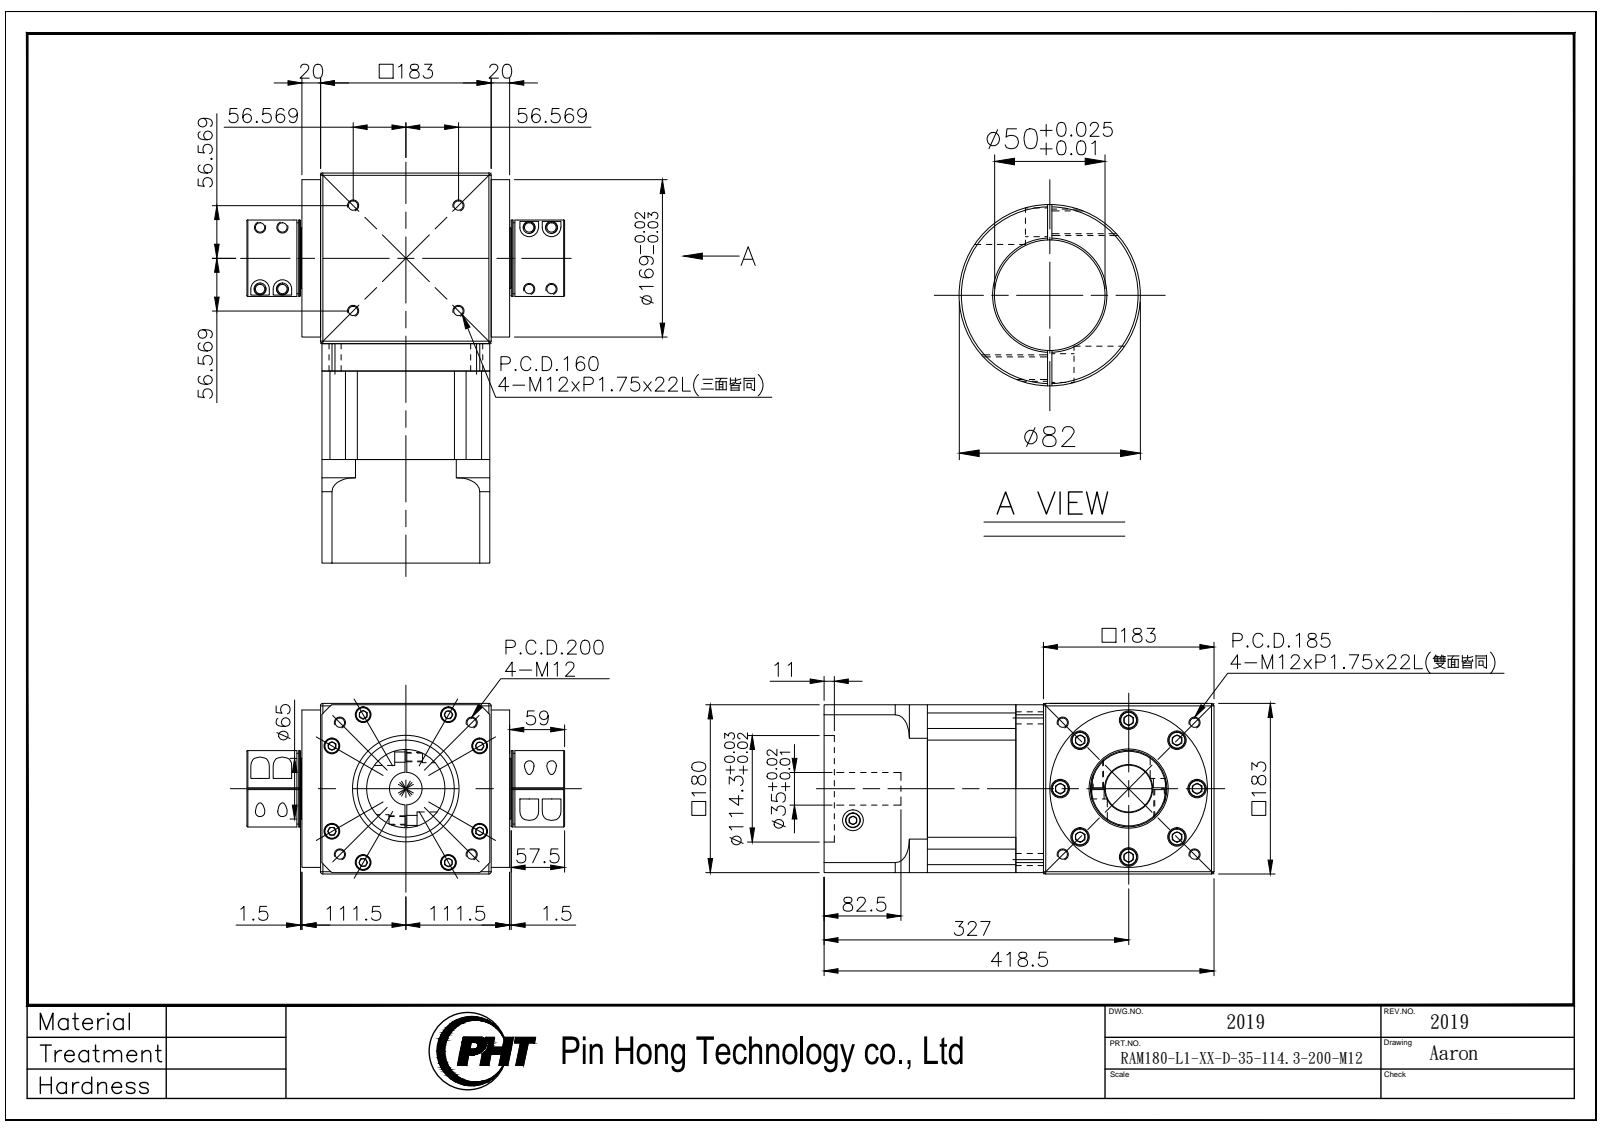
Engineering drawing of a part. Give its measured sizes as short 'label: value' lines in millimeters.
name: RA180-L1-XX-D-35-114.3-200-M12_2019
written by: SolidWorks 2016 (AUTOMOTIVE_DESIGN)
unit: mm
bodies: 4 solids, 1055 faces (475 planar, 368 cylindrical, 212 other)
size: 418.5 × 341 × 183
volume: 13 660 000 mm³; area: 881 416 mm²
holes: 20× ⌀10.2, 12× ⌀13, 8× ⌀11, 8× ⌀14, 8× ⌀17, 8× ⌀20, 2× ⌀22.5, 1× ⌀35, 1× ⌀50, 1× ⌀50.6, 1× ⌀56.5, 1× ⌀104
bosses: 12× ⌀18, 8× ⌀18.3, 8× ⌀16, 8× ⌀12, 1× ⌀169, 1× ⌀160, 1× ⌀85, 1× ⌀84
rounds: 8× R10, 4× R12.5, 1× R104, 1× R105, 1× R120
face distances: 1.5, 181.5, 183, 180, 95, 124.5, 29.5, 212.5, 21.5, 307.5
hole spacings: 91.5, 25.12, 26.38, 30.43, 56.25, 65.91, 73.5, 103.94
